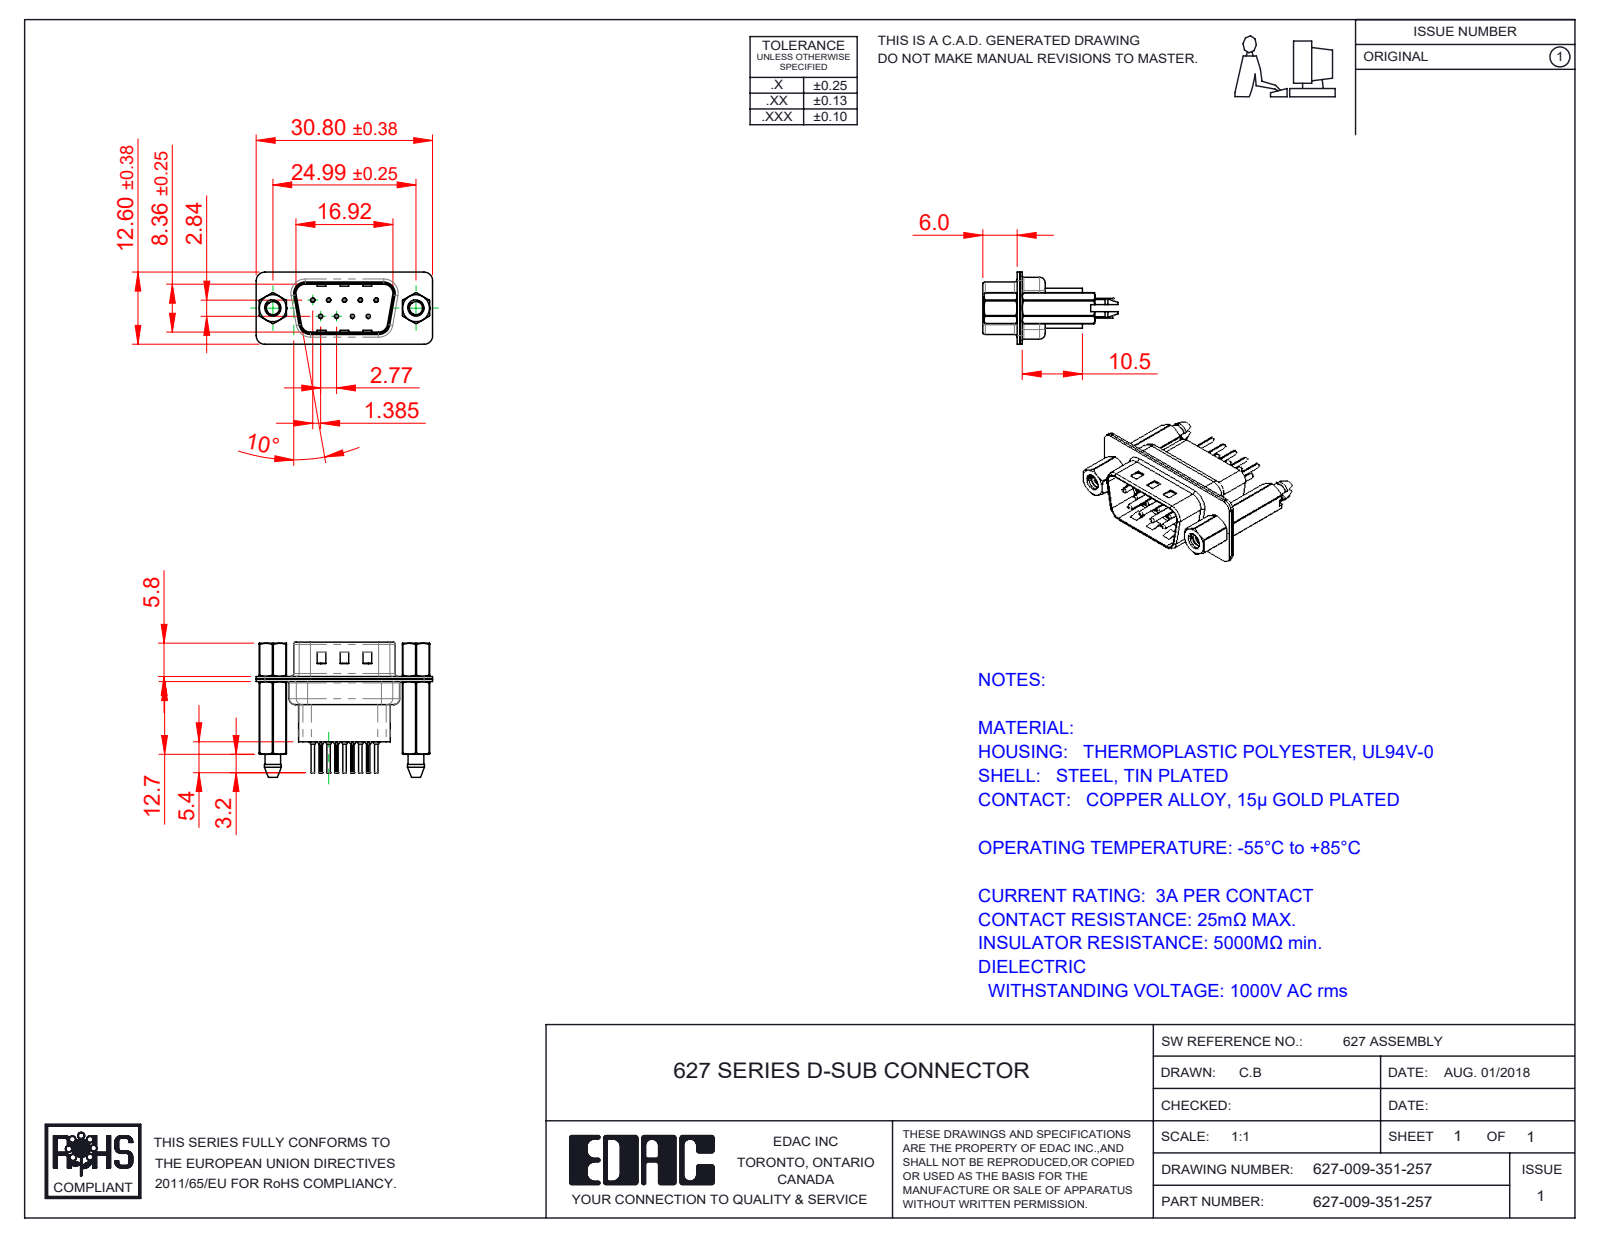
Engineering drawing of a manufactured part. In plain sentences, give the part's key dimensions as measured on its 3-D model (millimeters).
The part is named "627 Contact Row 1_41; 627 Shell Rear_09 Contacts; 627 Shell Front_09 Contacts; 627-009-351-257 (+4 more)". Its 3-D file was written by "SolidWorks 2020 (CONFIG_CONTROL_DESIGN)". It is 16 solids with 1420 faces: 377 planar, 600 cylindrical and 443 other. Overall it measures 30.8 by 23.6 by 12.6 millimeters. Its volume is 2 299 cubic millimeters and its surface area 5 905 square millimeters. Round holes: 9 of diameter 0.2, 9 of diameter 0.35, 9 of diameter 1.1, 9 of diameter 1.6, 2 of diameter 2.26, 2 of diameter 2.29, 2 of diameter 4, 2 of diameter 4.8. Round bosses or shafts: 9 of diameter 2, 9 of diameter 1.5, 9 of diameter 0.75, 9 of diameter 0.6, 2 of diameter 4.9, 2 of diameter 2.79. Partial cylindrical surfaces (rounded edges, fillets, slot ends): 20 of radius 1.5, 18 of radius 0.1, 12 of radius 2, 10 of radius 1.6, 8 of radius 0.5, 4 of radius 0.25, 4 of radius 0.6, 4 of radius 0.65. The main face-to-face distances are 0.45, 0.4, 0.9, 4.76, 0.82, 9.58, 1.4, 1.5, 0.68, 7.68. The hole center spacings are 3.16, 2.77, 5.54, 5.03, 5.04, 8.31, 7.48, 7.49.
